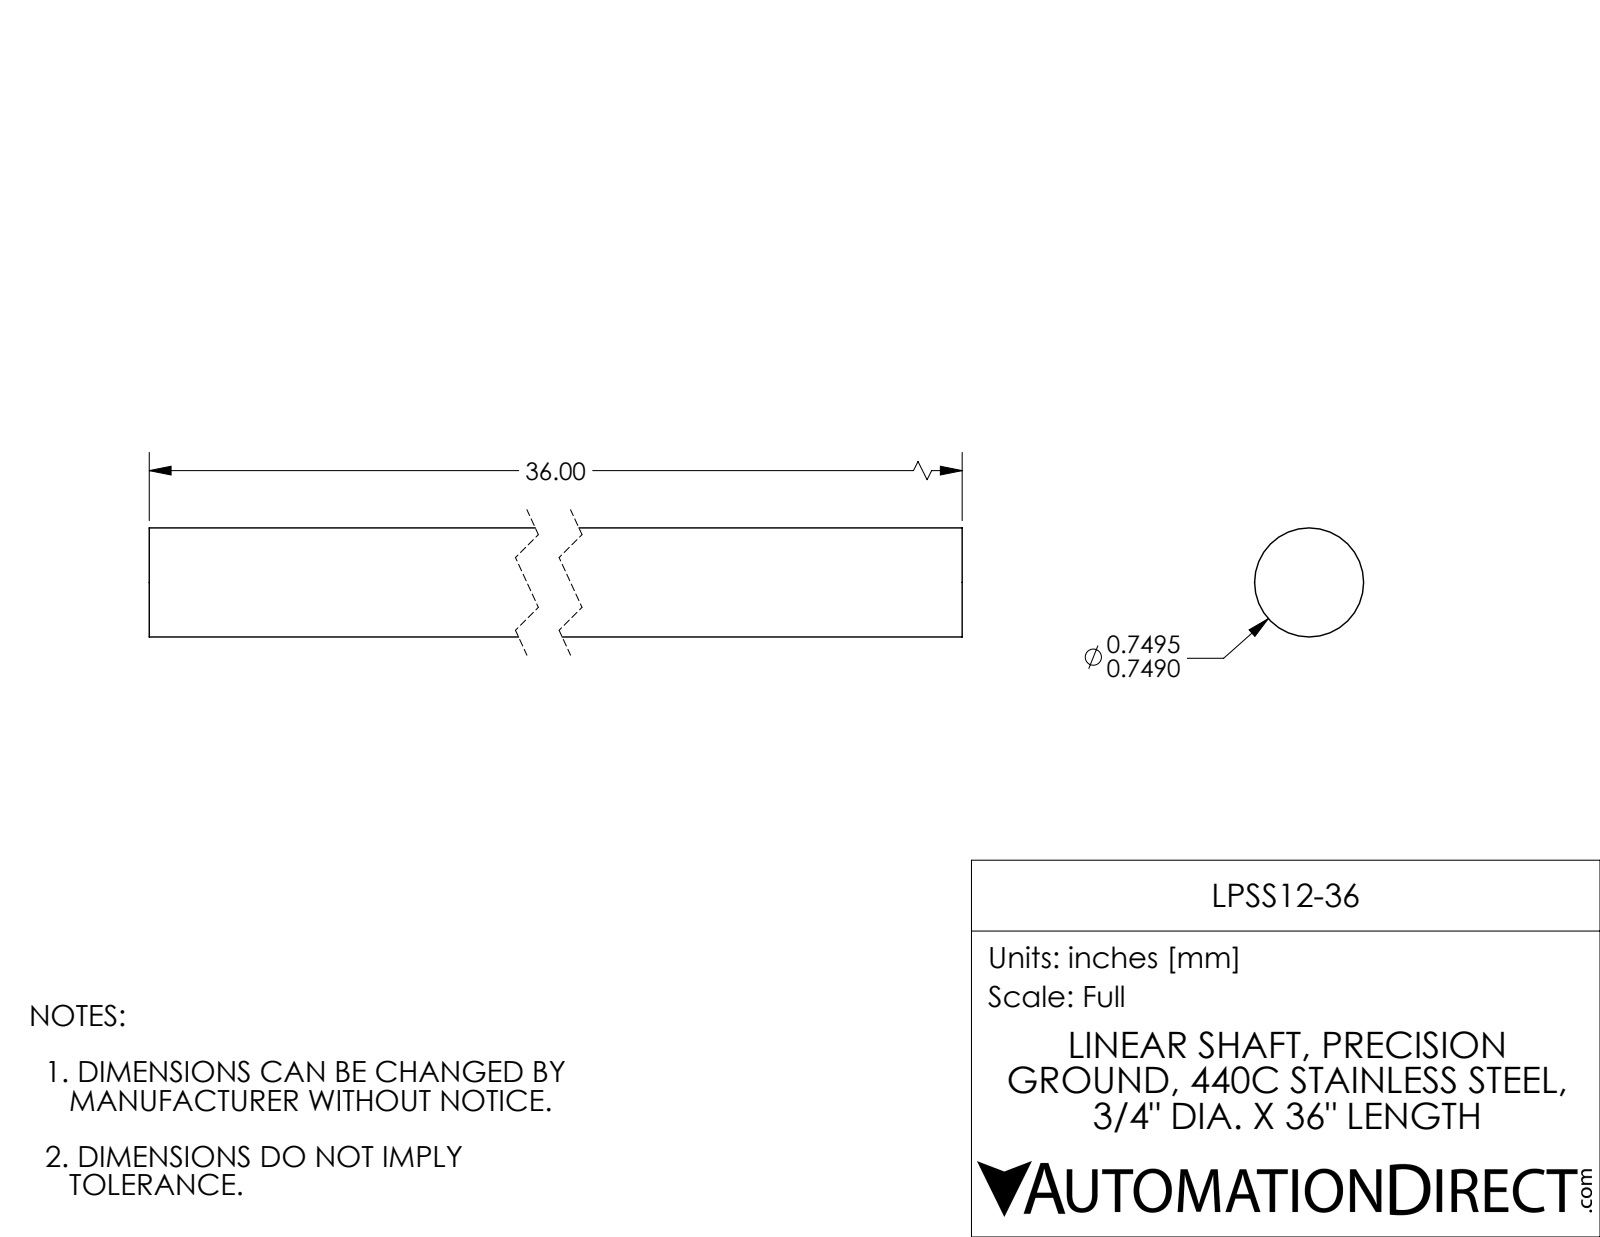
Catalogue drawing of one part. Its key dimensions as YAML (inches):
part_name: "LPSS12-36"
step_written_by: "SolidWorks 2017 (AUTOMOTIVE_DESIGN)"
units: inches
bodies: {solids: 1, faces: 4, planar: 2, cylindrical: 2, other: 0}
overall_size: [36, 0.749, 0.749]
volume: 15.88
surface_area: 85.65
round_bosses_or_shafts:
  - {diameter: 0.75, count: 1}
face_to_face_distances: [36]
